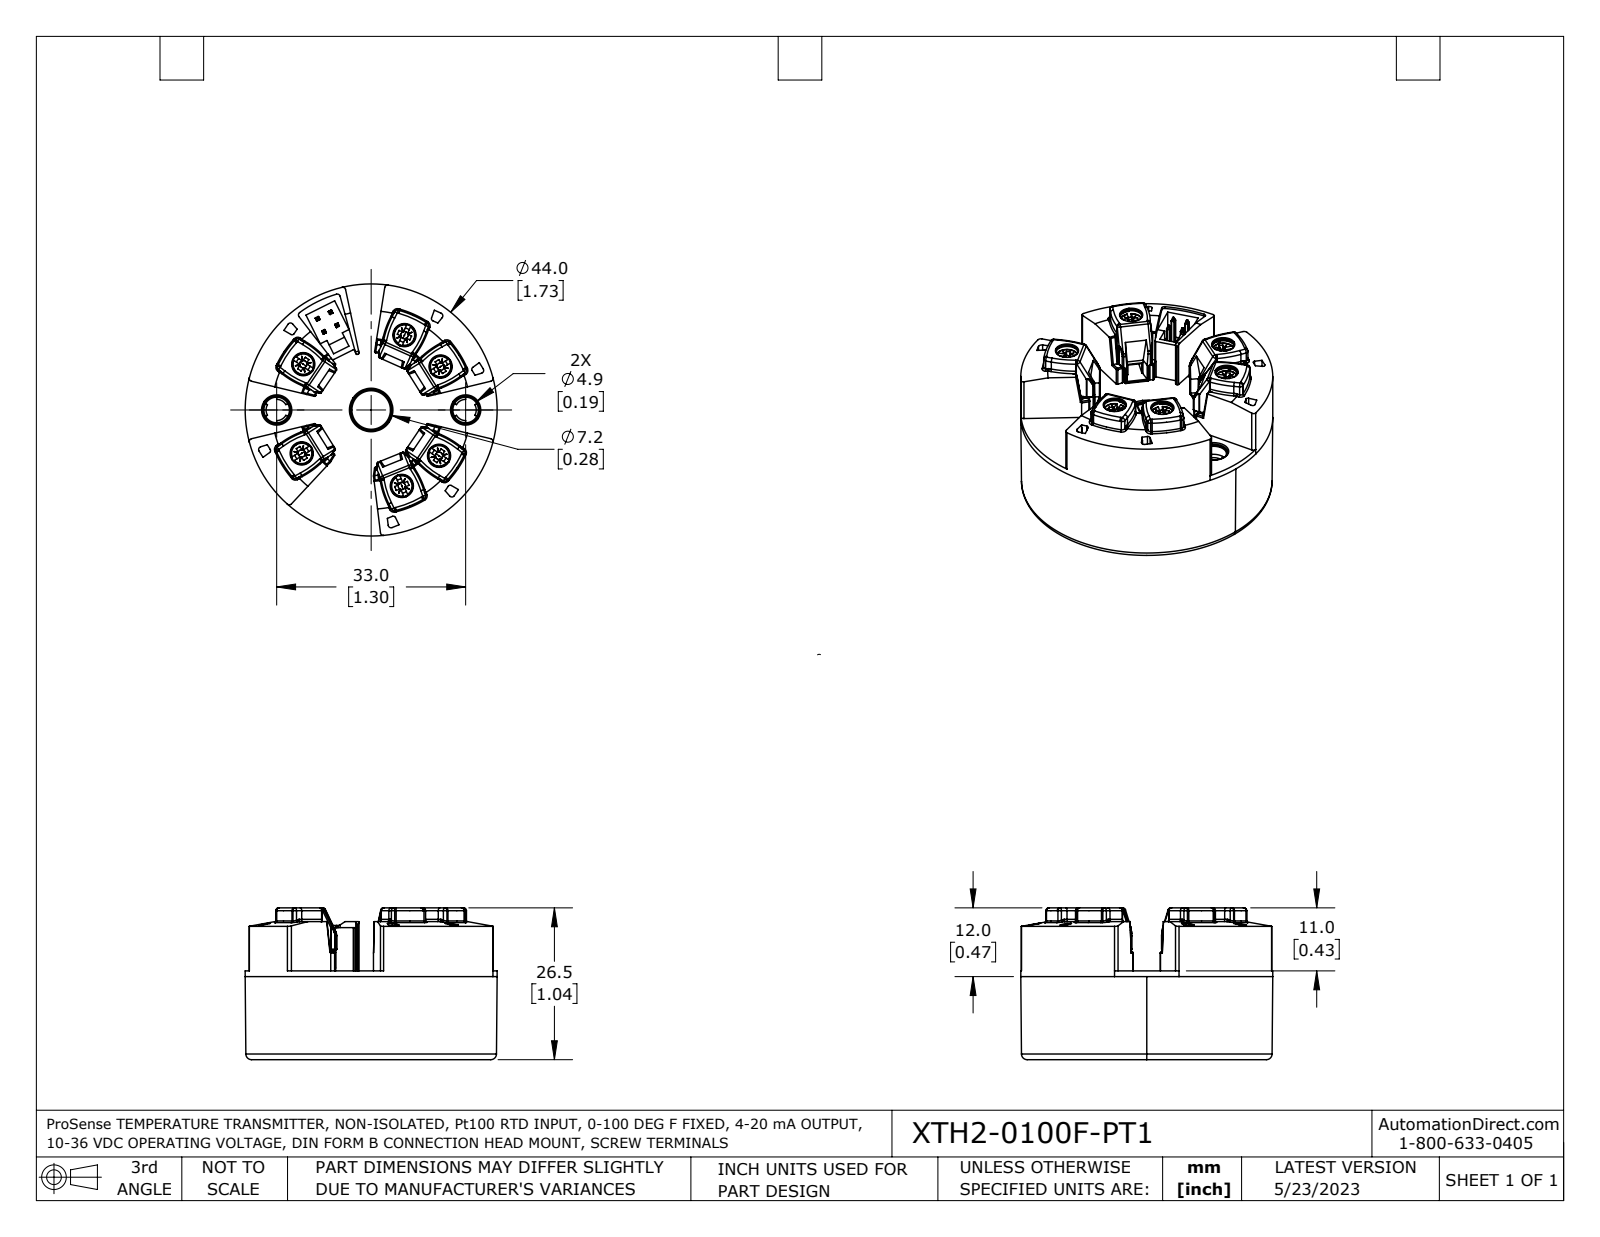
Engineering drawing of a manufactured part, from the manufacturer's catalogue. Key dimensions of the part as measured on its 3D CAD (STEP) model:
Part name (STEP PRODUCT): XTH2-0100F-PT1
STEP written by: SolidWorks 2021 (AUTOMOTIVE_DESIGN)
Units: inches
Bodies: 1 solid, 2500 faces (944 planar, 967 cylindrical, 589 other)
Overall size (bounding box): 1.732 × 1.732 × 1.043
Volume: 0.846 in³ · Surface area: 24.66 in²
Round holes (diameter × count): ⌀0.102 ×6, ⌀0.151 ×6, ⌀0.159 ×6, ⌀0.193 ×2, ⌀0.248 ×2, ⌀0.213 ×1, ⌀0.283 ×1, ⌀0.339 ×1, ⌀0.685 ×1
Round bosses / shafts (diameter × count): ⌀0.106 ×12, ⌀0.156 ×6, ⌀0.098 ×6, ⌀1.732 ×1, ⌀1.646 ×1, ⌀0.402 ×1
Partial cylindrical surfaces — rounded edges, fillets, slot ends (radius × count): R0.008 ×247, R0.02 ×144, R0.012 ×58, R0.004 ×48, R0.01 ×36, R0.006 ×18, R0.016 ×12, R0.592 ×12
Main face-to-face distances: 0.039, 0.571, 0.453, 0.118, 0.492, 0.61, 0.079, 0.531, 0.098, 0.067
Hole centre spacings: 0.563, 0.863, 0.329, 0.344, 0.364, 0.563, 0.613, 0.65
